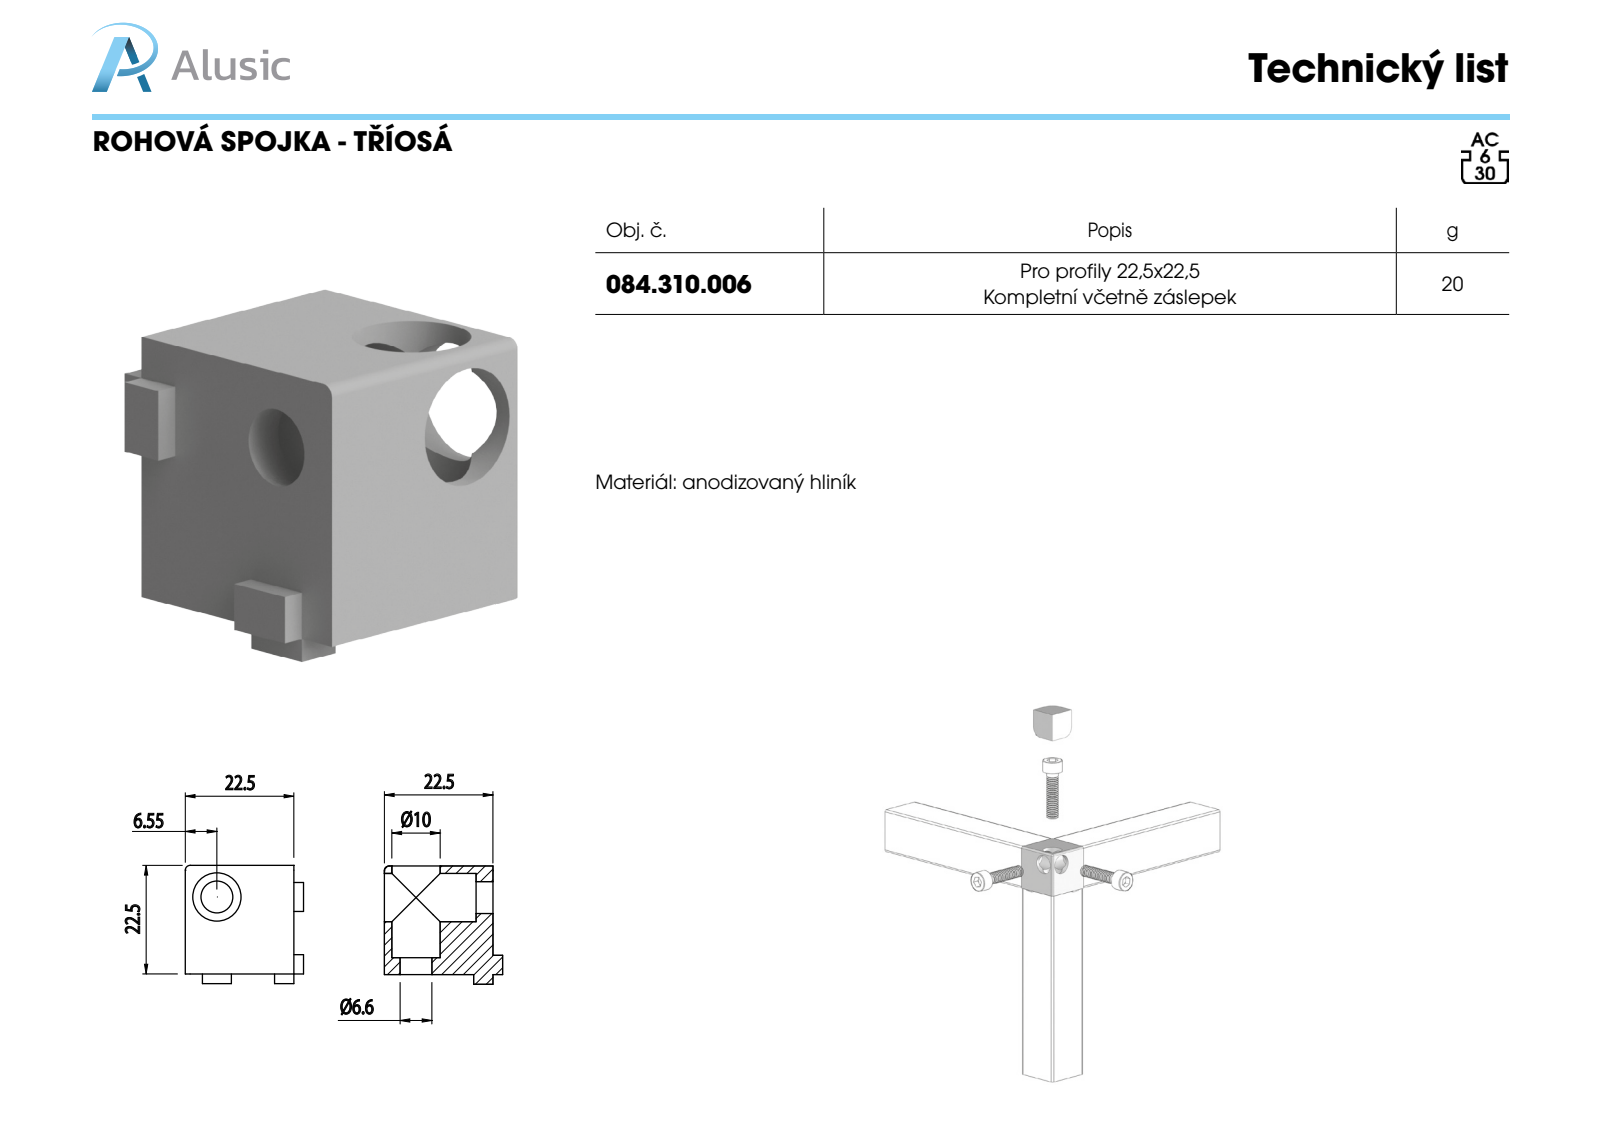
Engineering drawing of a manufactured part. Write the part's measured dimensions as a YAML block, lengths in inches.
part_name: "084.310.006"
step_written_by: "SolidWorks 2011 (CONFIG_CONTROL_DESIGN)"
units: inches
bodies: {solids: 1, faces: 61, planar: 39, cylindrical: 21, other: 1}
overall_size: [0.965, 0.965, 0.965]
volume: 0.503
surface_area: 6.513
round_holes:
  - {diameter: 0.26, count: 3}
  - {diameter: 0.394, count: 3}
partial_cylinders:
  - {radius: 0.039, count: 3}
face_to_face_distances: [0.886, 0.965, 0.079, 0.748, 0.138, 0.217, 0.236, 0.589, 0.728, 0.02]
